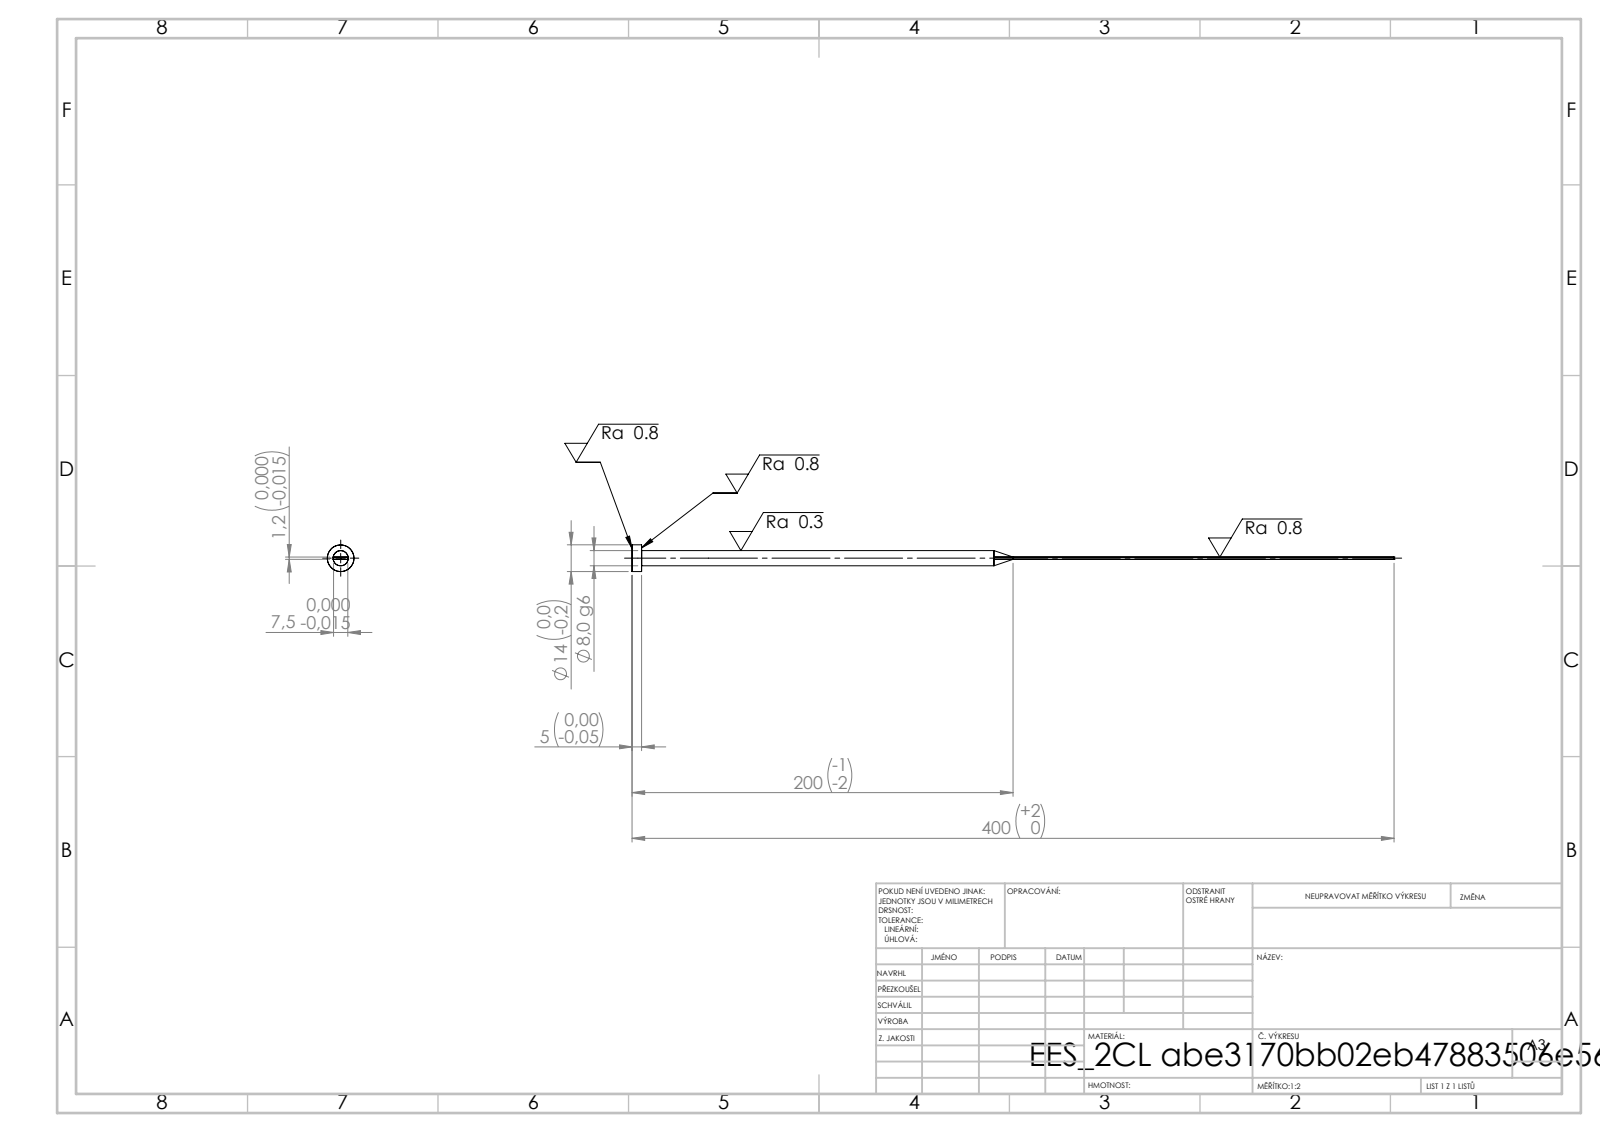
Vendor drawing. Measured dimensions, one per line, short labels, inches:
written by: SolidWorks 2019 (CONFIG_CONTROL_DESIGN)
unit: in
bodies: 1 solid, 15 faces (7 planar, 4 cylindrical, 4 other)
size: 15.748 × 0.551 × 0.551
volume: 0.741 in³; area: 13.68 in²
bosses: 1× ⌀0.551, 1× ⌀0.315
face distances: 0.047, 0.295, 0.197, 15.748, 15.551
